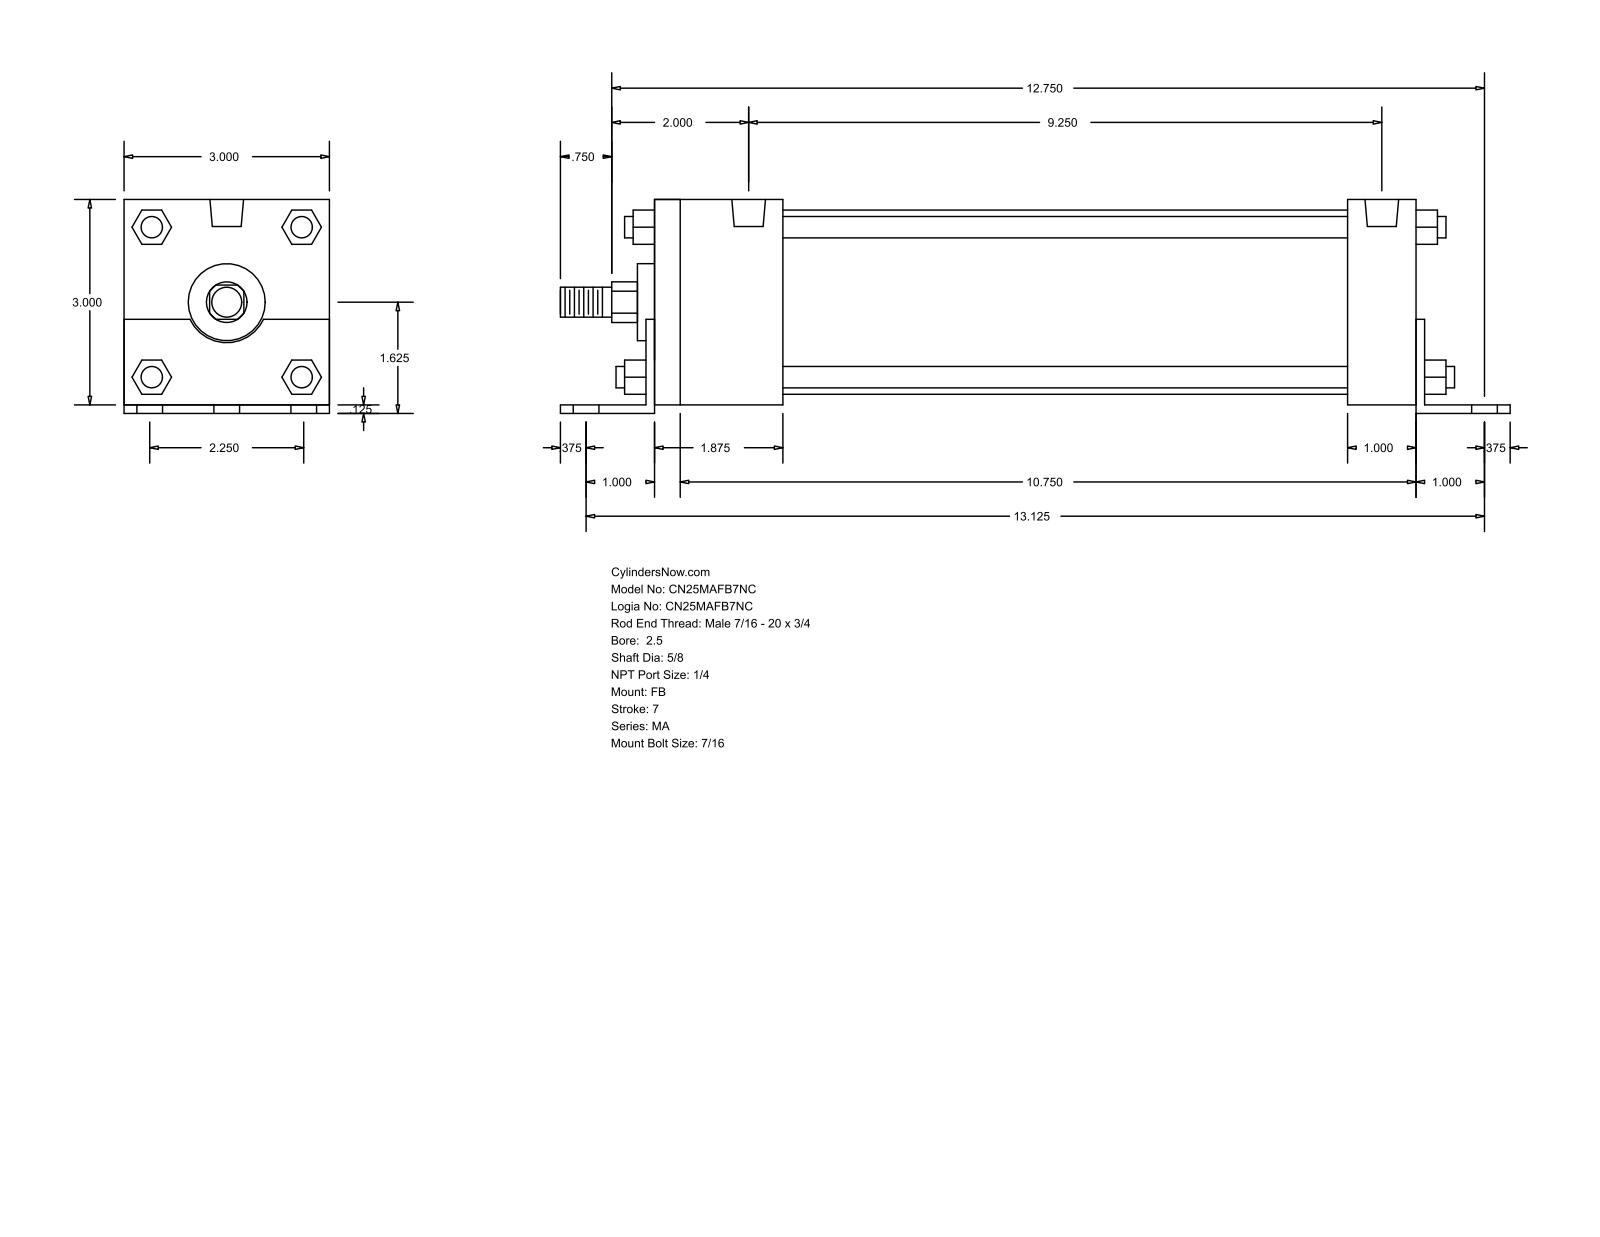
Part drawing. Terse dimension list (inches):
name: MA_FB__0250_0.625
written by: GSSL Pune (CONFIG_CONTROL_DESIGN)
unit: in
bodies: 0 solids, 140 faces (105 planar, 35 cylindrical, 0 other)
size: 13.875 × 3.125 × 3
holes: 6× ⌀0.437, 4× ⌀0.313, 2× ⌀0.492
bosses: 4× ⌀0.313, 1× ⌀2.69, 1× ⌀1.125, 1× ⌀0.625, 1× ⌀0.437
rounds: 1× R0.297, 1× R0.593
face distances: 3, 0.125, 3.125, 11.125, 11.375, 0.125, 11.25, 1.875, 1, 11.25
hole spacings: 1.125, 13.173, 13.125, 1.875, 2.25, 2.628, 9.25, 10.809
